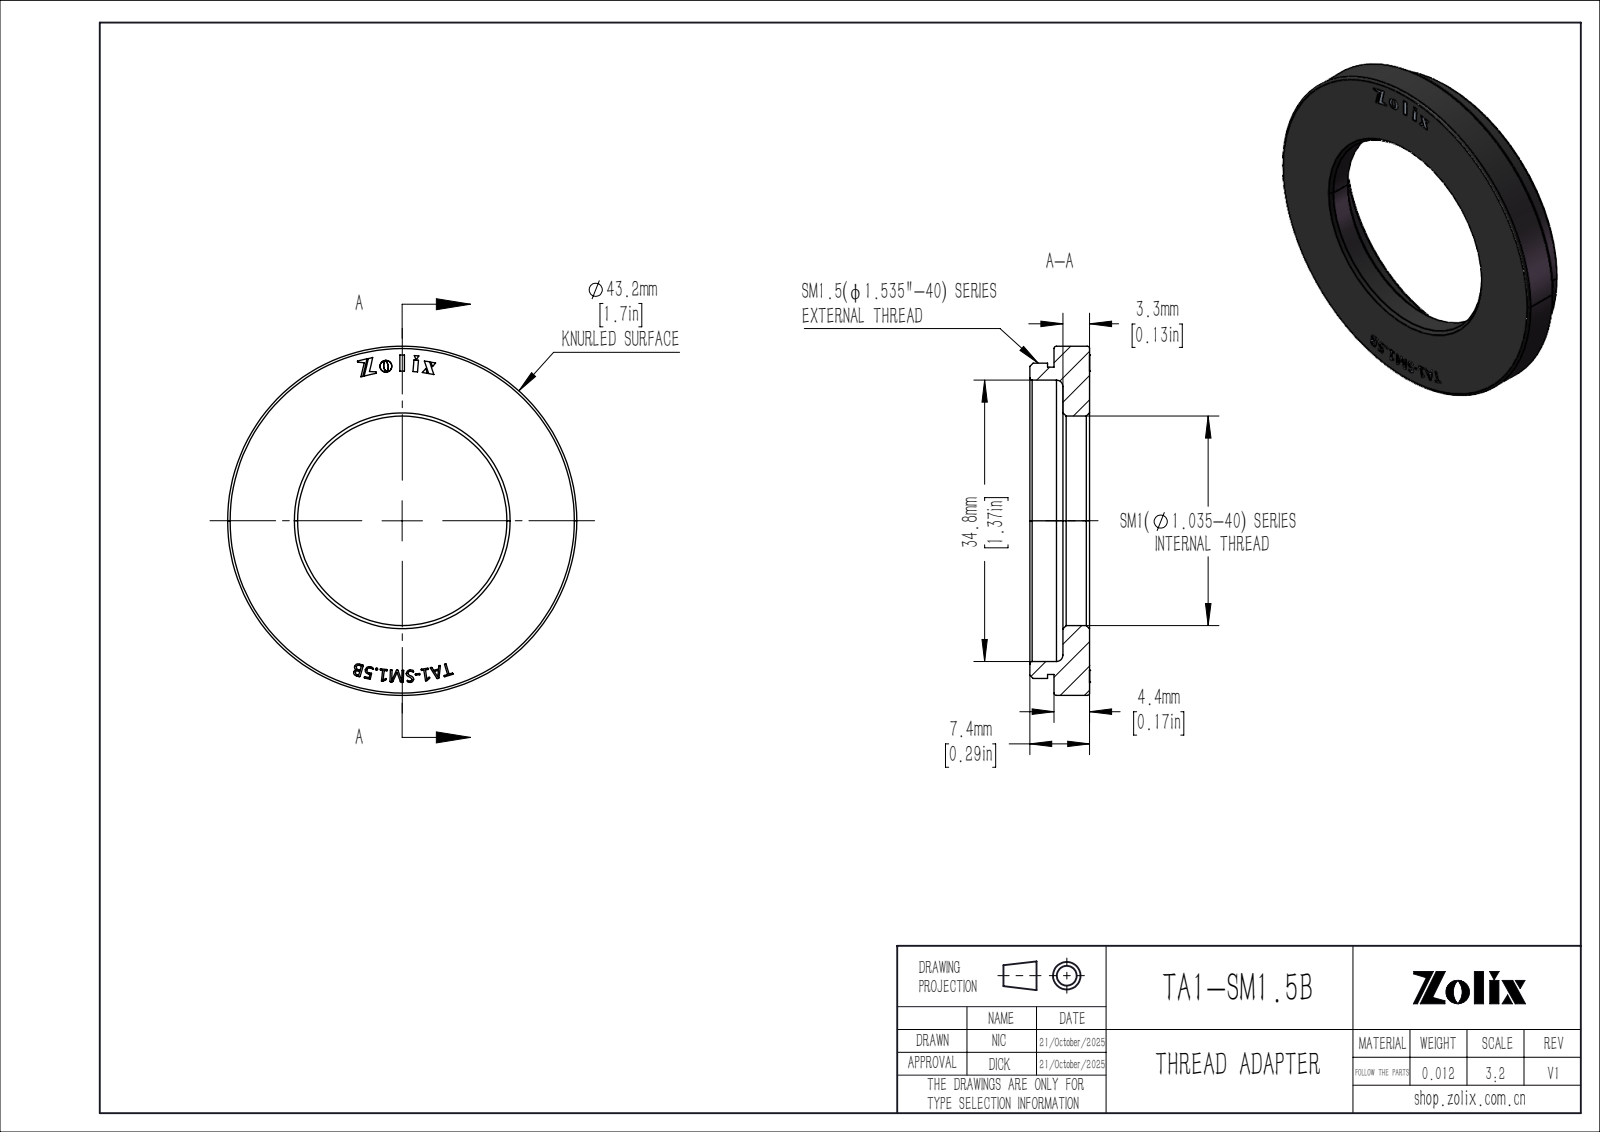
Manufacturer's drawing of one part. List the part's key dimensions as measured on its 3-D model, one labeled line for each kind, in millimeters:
Part name (STEP PRODUCT): TA1-SM1.5B
STEP written by: SolidWorks 2020 (CONFIG_CONTROL_DESIGN)
Units: millimetres
Bodies: 1 solid, 342 faces (229 planar, 10 cylindrical, 103 other)
Overall size (bounding box): 43.2 × 43.2 × 7.4
Volume: 4 331 mm³ · Surface area: 3 526 mm²
Round holes (diameter × count): ⌀25.9 ×1, ⌀34.8 ×1
Round bosses / shafts (diameter × count): ⌀43.2 ×1, ⌀39 ×1, ⌀38 ×1
Main face-to-face distances: 3.3, 1.1, 4.4, 3, 4.1, 7.4, 2.2, 0.8, 1.9, 5.2
